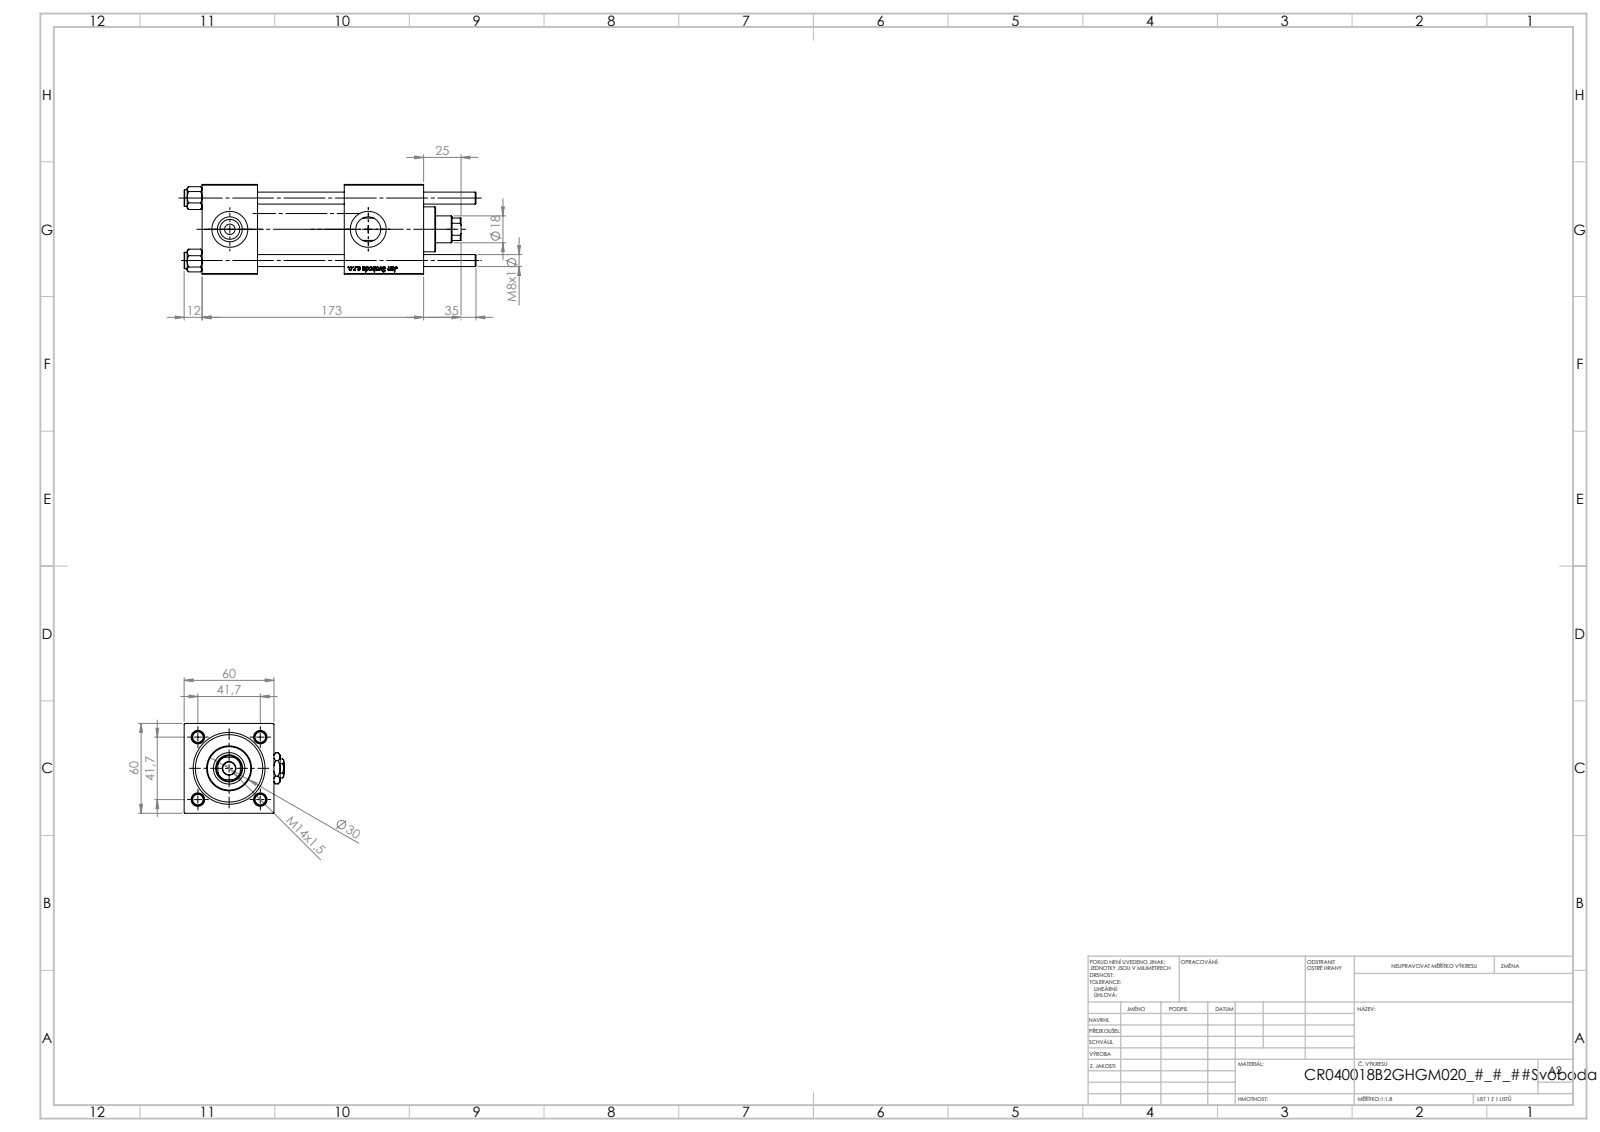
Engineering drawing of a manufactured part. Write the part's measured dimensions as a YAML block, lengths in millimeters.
part_name: "V215CR_VCP_B; V215_VC_A; V215CR_B_TYCINKA; Zatka_pro_OIL_PORT (+2 more)"
step_written_by: "SolidWorks 2019 (CONFIG_CONTROL_DESIGN)"
units: millimeters
bodies: {solids: 12, faces: 1211, planar: 457, cylindrical: 84, other: 670}
overall_size: [195, 67, 60]
volume: 412603
surface_area: 115406
round_holes:
  - {diameter: 8, count: 4}
  - {diameter: 7, count: 2}
  - {diameter: 16.66, count: 2}
  - {diameter: 24, count: 2}
  - {diameter: 8.5, count: 1}
  - {diameter: 18, count: 1}
  - {diameter: 21, count: 1}
  - {diameter: 31, count: 1}
  - {diameter: 40, count: 1}
  - {diameter: 45, count: 1}
round_bosses_or_shafts:
  - {diameter: 11, count: 4}
  - {diameter: 46, count: 1}
  - {diameter: 30, count: 1}
partial_cylinders:
  - {radius: 8.5, count: 1}
face_to_face_distances: [60, 37, 148, 111, 58, 53, 95, 119.3, 82.3, 24.3]
hole_center_spacings: [29.49, 41.7, 58.97, 92.5]
